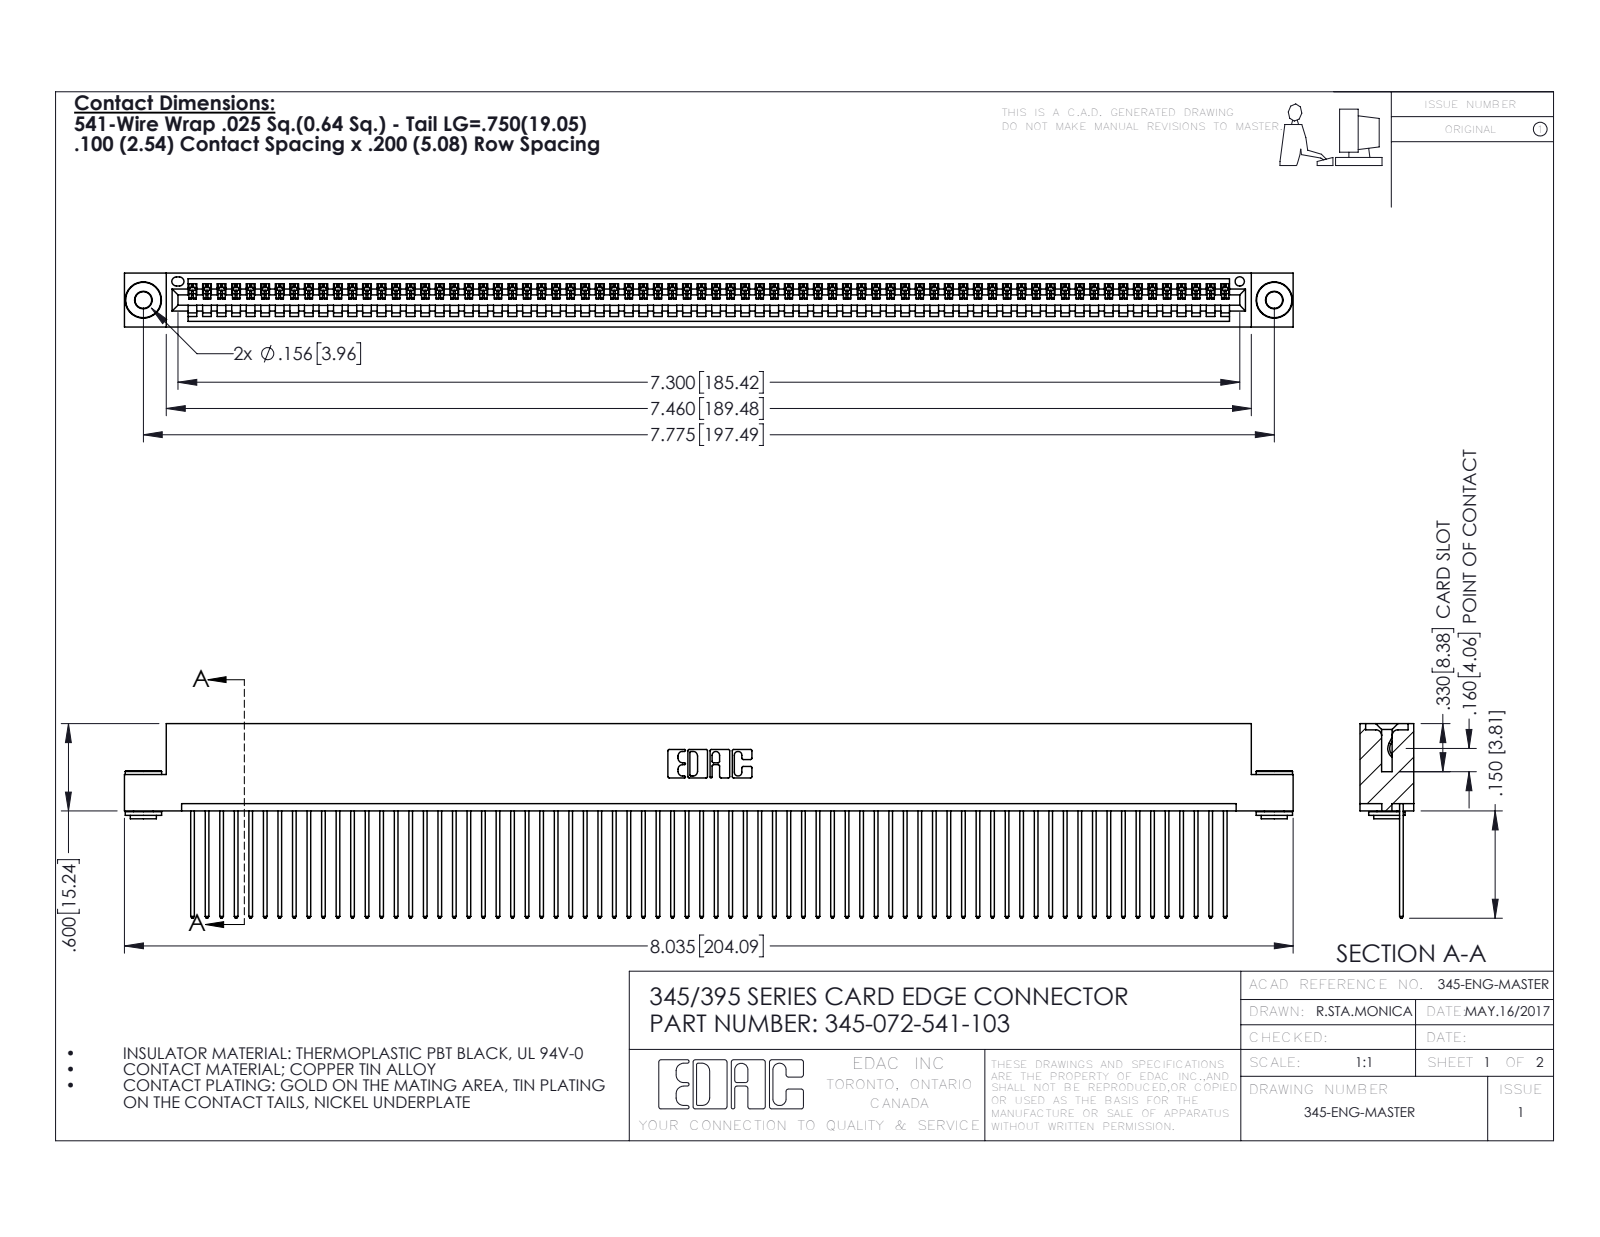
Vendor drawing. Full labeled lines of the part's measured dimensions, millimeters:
Part name (STEP PRODUCT): 345-072-541-103; 345-250-002_345-250-002-102; 345 Part_Flush Mounting Lugs - 0.156 Dia-TH; 345-292-001_345-293-141
STEP written by: SolidWorks 2016 (CONFIG_CONTROL_DESIGN)
Units: millimetres
Bodies: 75 solids, 4340 faces (2970 planar, 1362 cylindrical, 8 other)
Overall size (bounding box): 204.1 × 34 × 9.4
Volume: 19 890 mm³ · Surface area: 28 450 mm²
Round holes (diameter × count): ⌀2.9 ×2, ⌀4 ×2, ⌀1.6 ×1
Round bosses / shafts (diameter × count): ⌀6.4 ×2, ⌀4.6 ×2, ⌀3.5 ×2
Partial cylindrical surfaces — rounded edges, fillets, slot ends (radius × count): R0.2 ×144, R0.3 ×144, R0.3 ×22, R0.2 ×6, R0.8 ×6, R0.7 ×3, R0.8 ×2, R1 ×2
Main face-to-face distances: 1.8, 7.6, 0.6, 2.5, 6.9, 9.4, 5.1, 5.7, 3.8, 1.8
Hole centre spacings: 6.9, 191.5, 197.5
